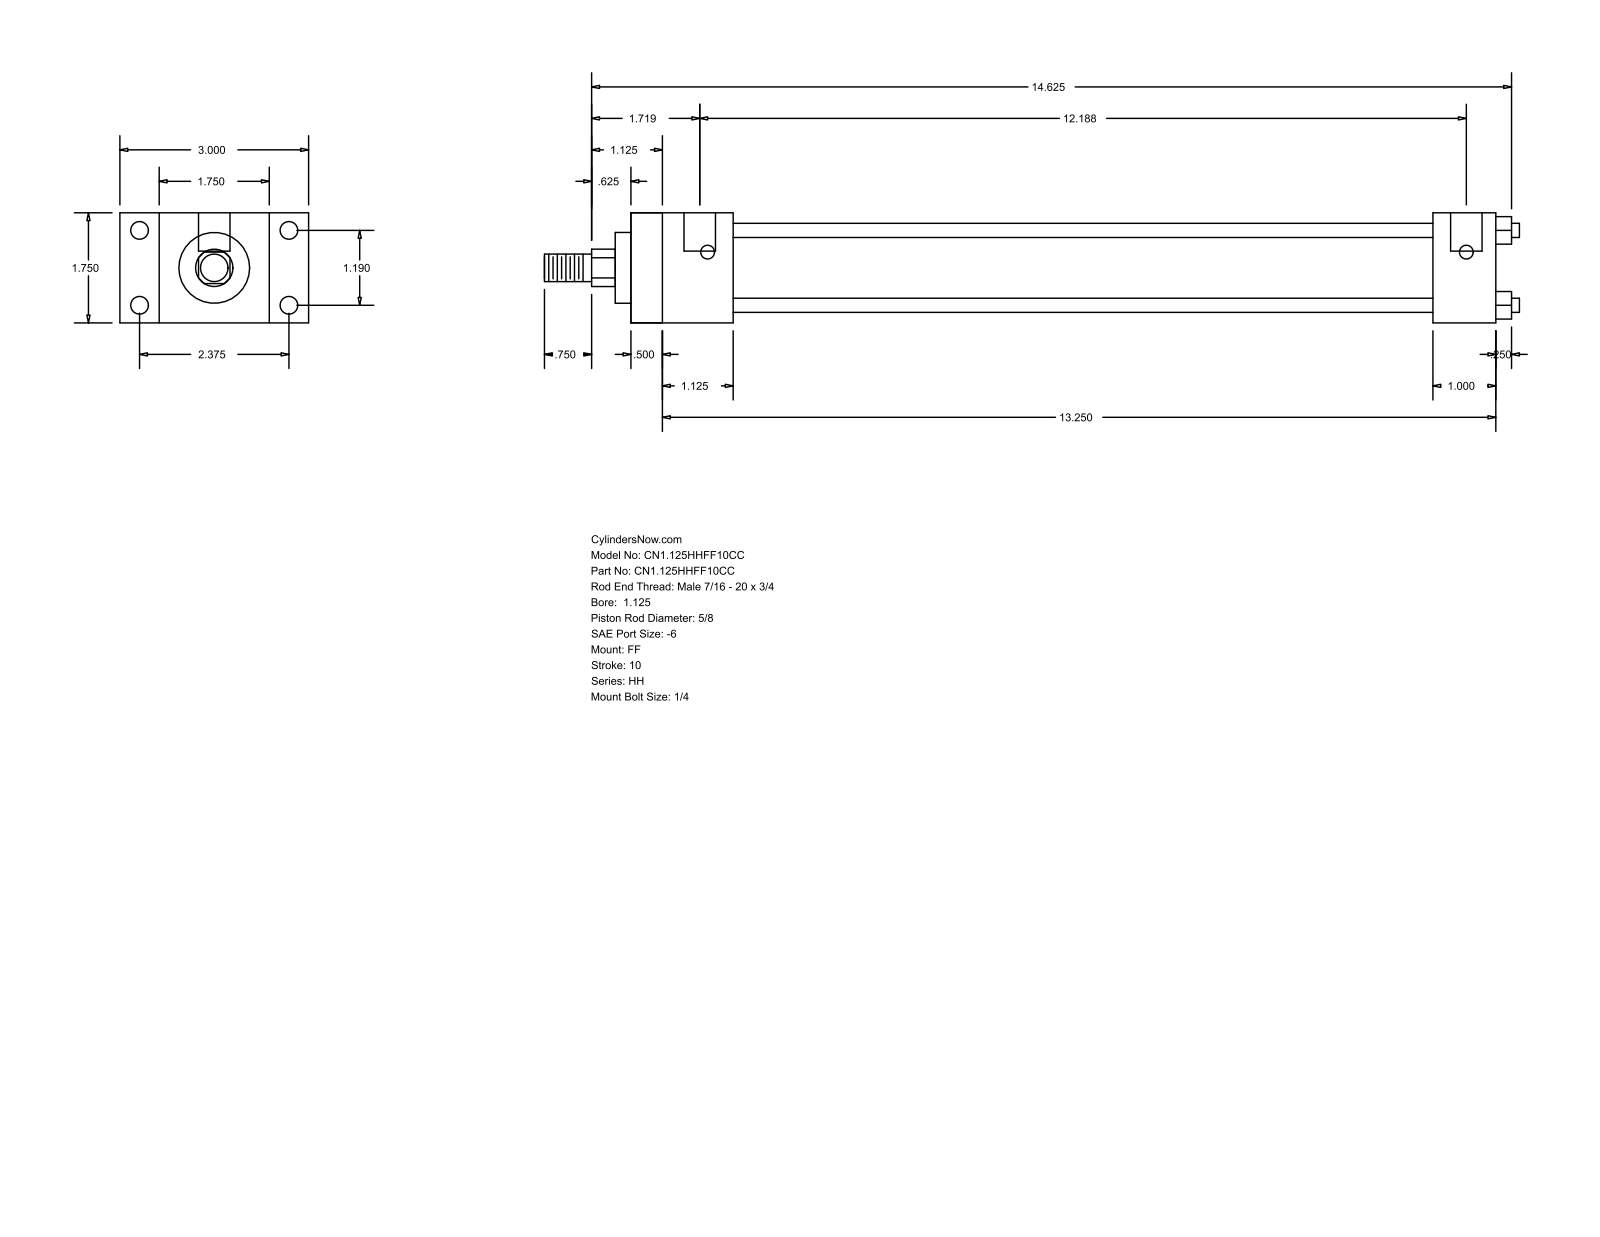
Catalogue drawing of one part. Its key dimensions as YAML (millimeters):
part_name: "HH_FF__0112_0.625"
step_written_by: "GSSL Pune (CONFIG_CONTROL_DESIGN)"
units: millimeters
bodies: {solids: 0, faces: 92, planar: 64, cylindrical: 28, other: 0}
overall_size: [393.7, 76.2, 44.45]
round_holes:
  - {diameter: 5.56, count: 4}
  - {diameter: 7.14, count: 4}
  - {diameter: 12.7, count: 2}
round_bosses_or_shafts:
  - {diameter: 5.71, count: 4}
  - {diameter: 34.92, count: 1}
  - {diameter: 28.57, count: 1}
  - {diameter: 15.88, count: 1}
  - {diameter: 11.11, count: 1}
partial_cylinders:
  - {radius: 7.54, count: 1}
face_to_face_distances: [44.46, 349.24, 12.69, 336.55, 15.87, 28.58, 60.33, 41.27, 323.85, 311.16]
hole_center_spacings: [30.22, 60.32, 67.47, 306.39, 3.17, 309.56]
